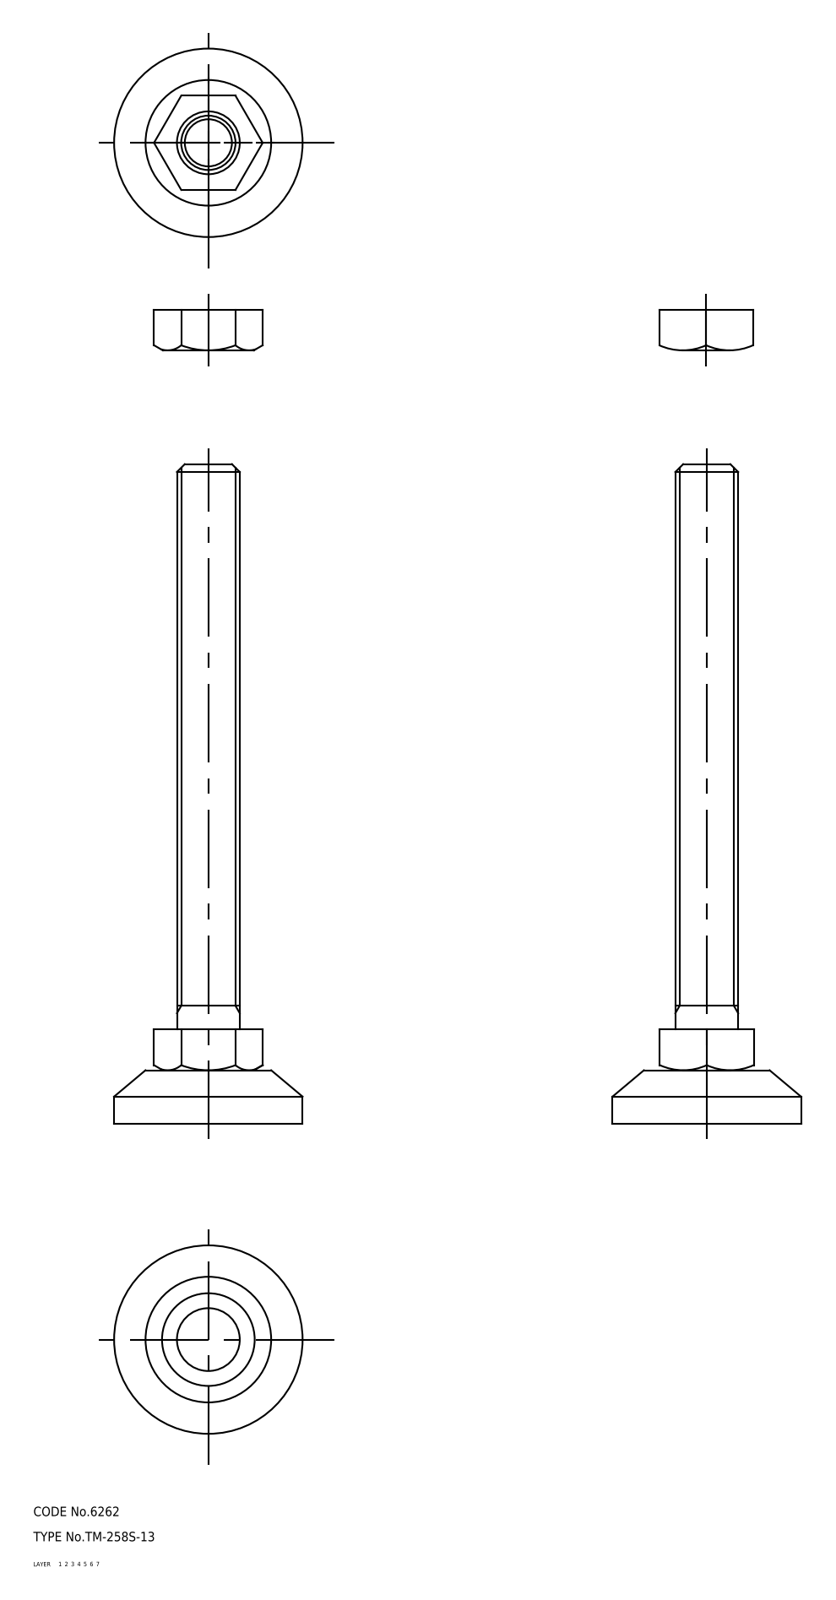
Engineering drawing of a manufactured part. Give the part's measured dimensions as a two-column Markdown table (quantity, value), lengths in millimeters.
| quantity | value |
| --- | --- |
| part name | 67112371; 67112384; 67112397 |
| STEP written by | CADfix (AUTOMOTIVE_DESIGN) |
| units | millimeters |
| bodies | 3 solids, 67 faces (0 planar, 0 cylindrical, 67 other) |
| overall size | 210 × 60 × 60 |
| volume | 105 188 mm³ |
| surface area | 26 610 mm² |
